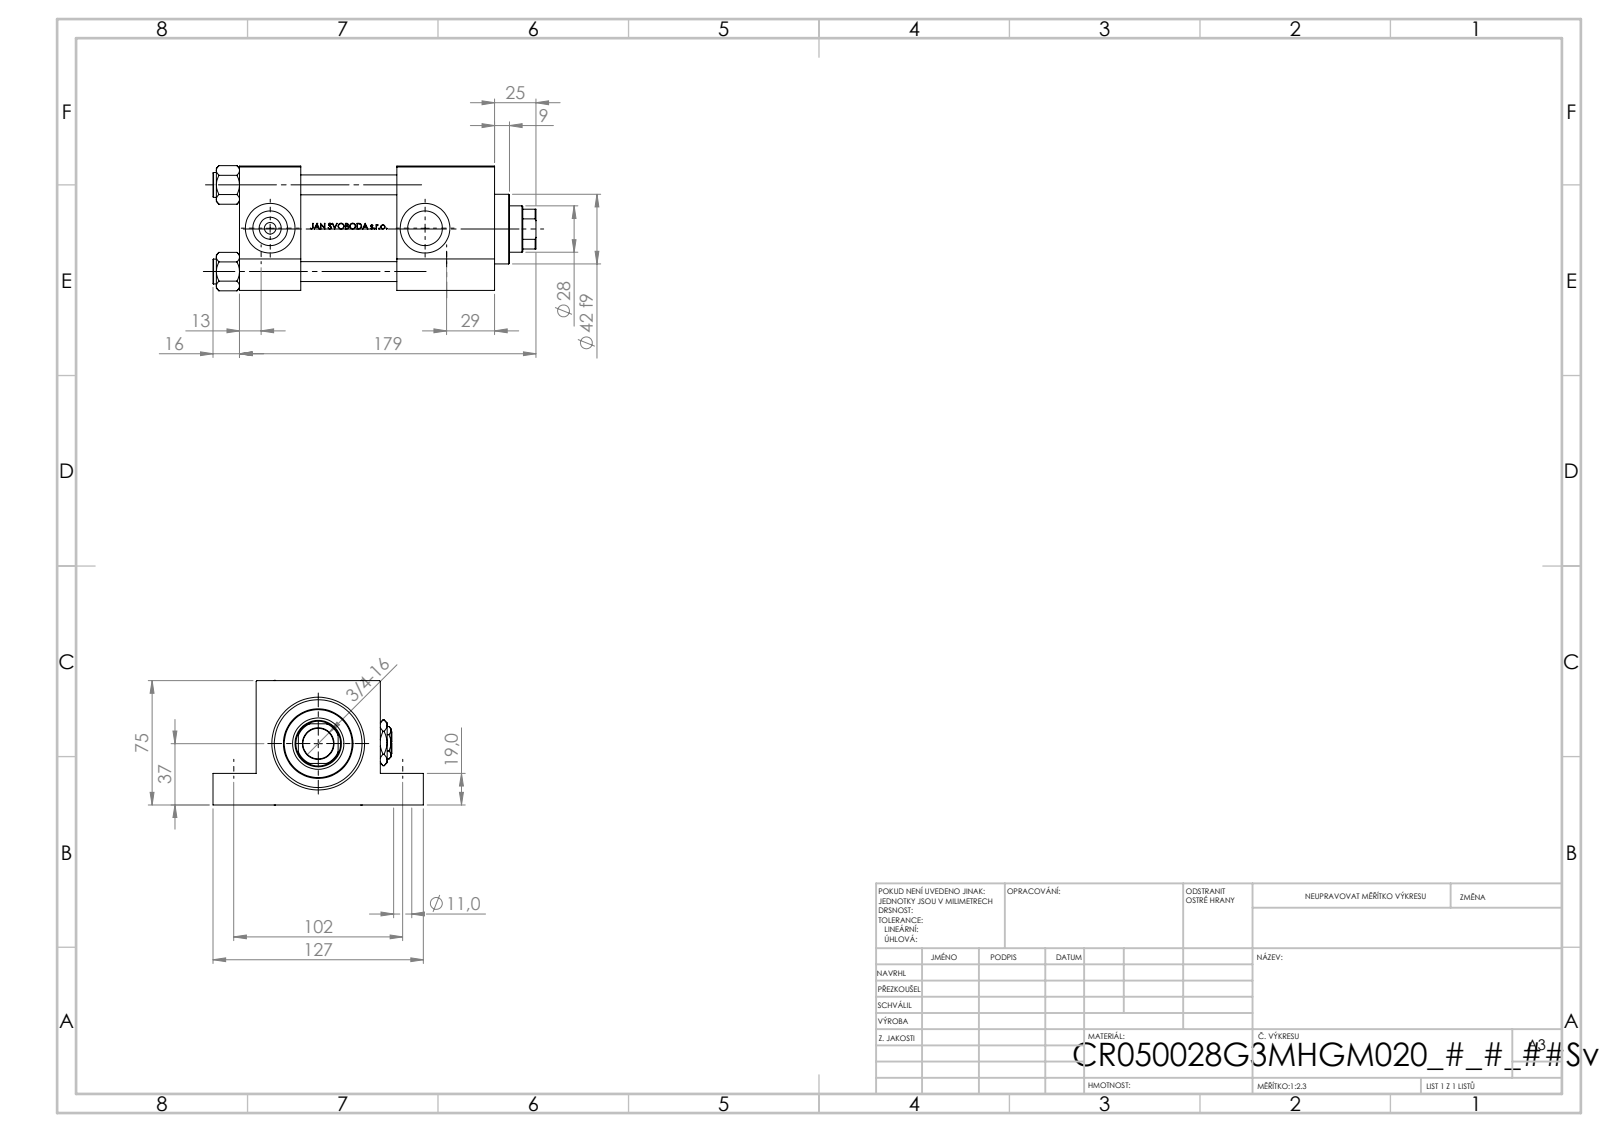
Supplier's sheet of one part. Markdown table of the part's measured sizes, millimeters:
| quantity | value |
| --- | --- |
| part name | V215CR_VCP_G; V215CR_G_Body; V215CR_G_TYCINKA; V215_VC_A (+2 more) |
| STEP written by | SolidWorks 2019 (CONFIG_CONTROL_DESIGN) |
| units | millimeters |
| bodies | 13 solids, 1183 faces (477 planar, 132 cylindrical, 574 other) |
| overall size | 195 × 127 × 75.54 |
| volume | 762 343 mm³ |
| surface area | 167 563 mm² |
| round holes (diameter × count) | 12 × 4, 11 × 3, 7 × 2, 20.96 × 2, 30 × 2, 11 × 1, 18.5 × 1, 28 × 1, 31 × 1, 41 × 1, 50 × 1, 53 × 1 |
| round bosses / shafts (diameter × count) | 15 × 4, 56 × 1, 42 × 1 |
| partial cylindrical surfaces (radius × count) | 13.5 × 1 |
| main face-to-face distances | 75, 37, 154, 117, 19, 56, 95, 58, 59, 26 |
| hole center spacings | 52.3, 36.63, 37.34, 73.96, 102, 112, 151.49, 93.5 |
